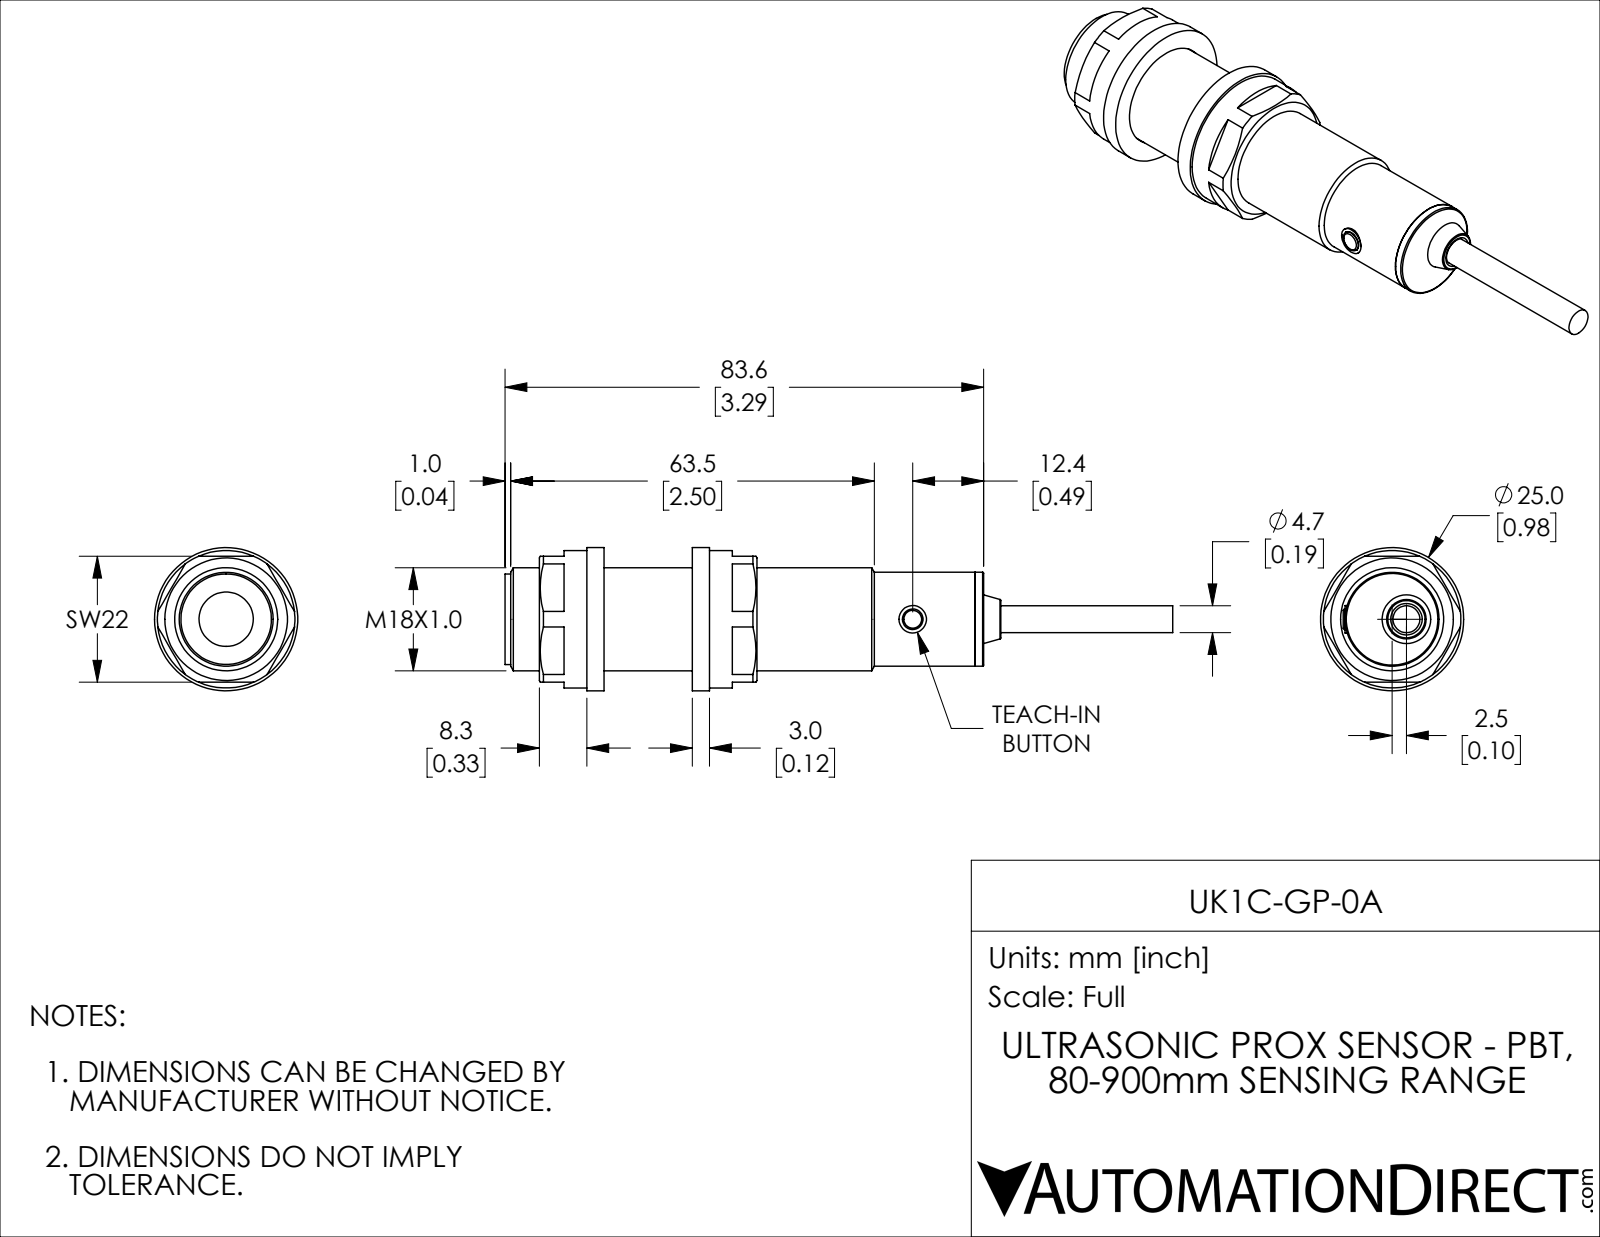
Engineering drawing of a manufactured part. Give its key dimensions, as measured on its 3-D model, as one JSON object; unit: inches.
{"part_name": "UK1C-GP-0A", "step_written_by": "SolidWorks 2018 (AUTOMOTIVE_DESIGN)", "units": "inches", "bodies": {"solids": 10, "faces": 107, "planar": 49, "cylindrical": 40, "other": 18}, "overall_size": [4.591, 0.984, 0.984], "volume_in3": 1.539, "surface_area_in2": 17.7, "round_holes": [[0.185, 2], [0.142, 1], [0.374, 1], [0.709, 1], [0.717, 1]], "round_bosses_or_shafts": [[0.984, 1], [0.945, 1], [0.646, 1], [0.622, 1], [0.213, 1], [0.189, 1]], "face_to_face_distances": [0.118, 0.724, 0.843, 2.669, 1.827, 0.524, 1.366, 3.193, 0.642, 2.551], "hole_center_spacings": [0.098]}
